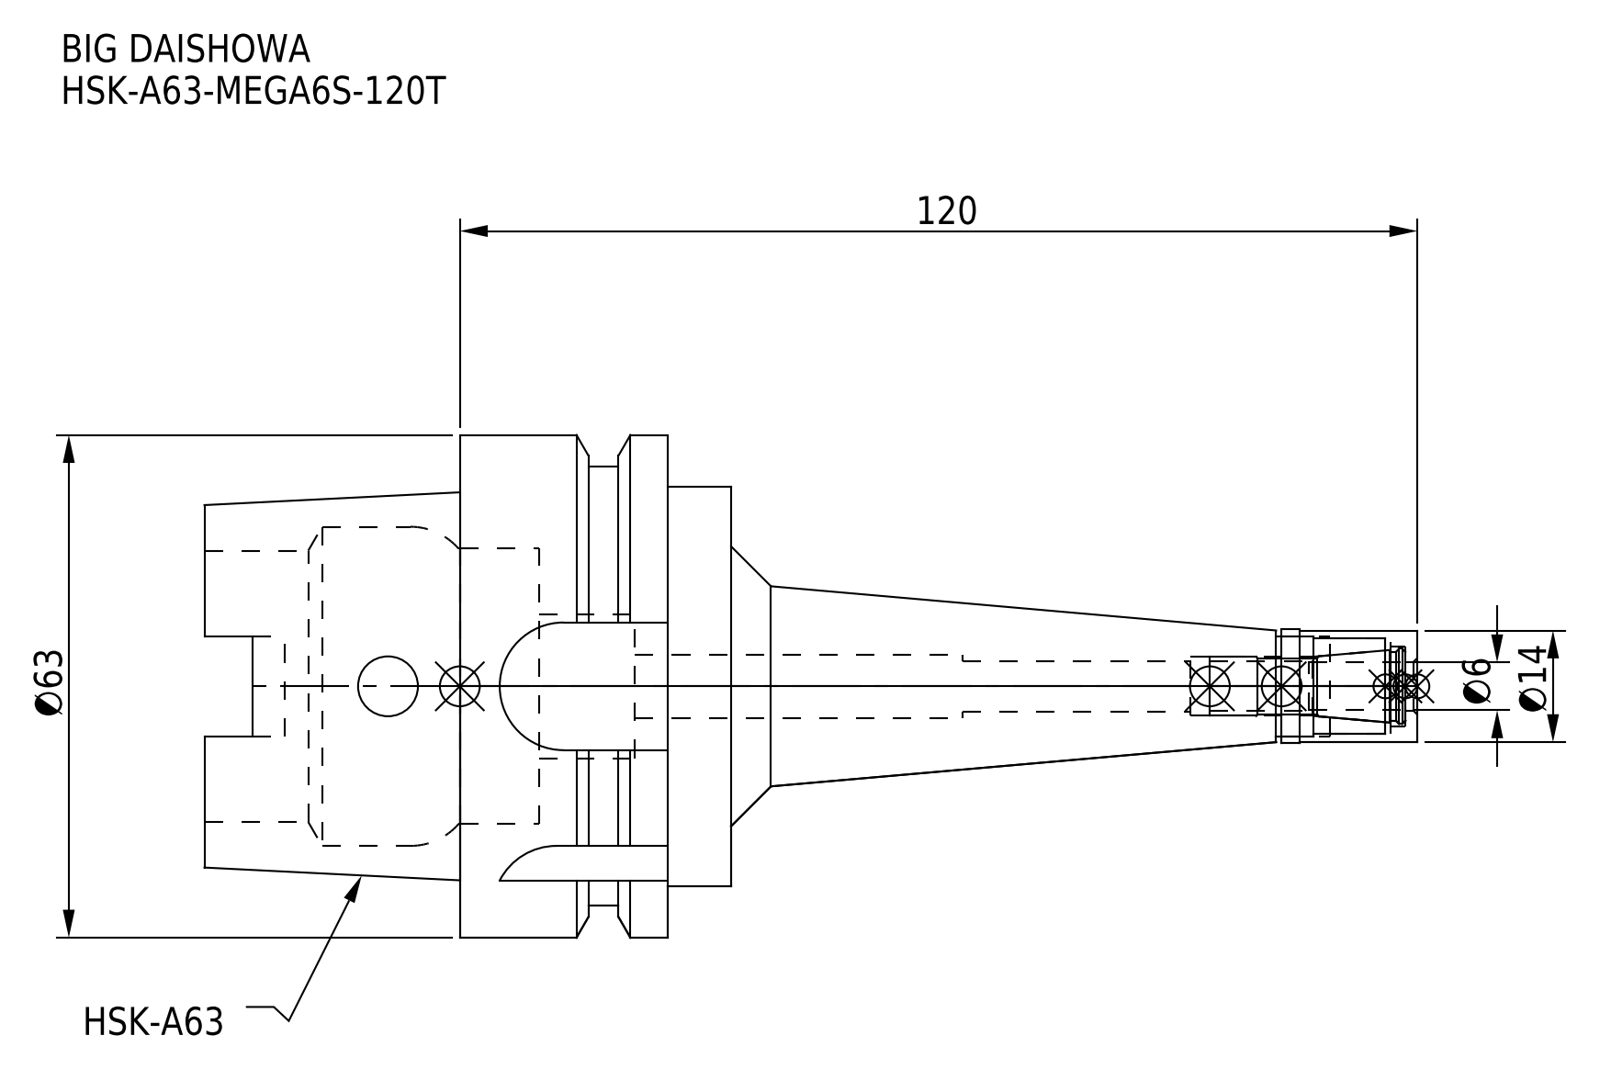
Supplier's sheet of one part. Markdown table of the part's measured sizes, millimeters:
| quantity | value |
| --- | --- |
| part name | HA63MS06120T-060_ASM.stp; HSK-A63-MEGA6S-120T-060.stp; MGN6S_1.stp; HSK-A63-MEGA6S-120T_1.stp (+3 more) |
| STEP written by | SolidWorks 2019 (CONFIG_CONTROL_DESIGN) |
| units | millimeters |
| bodies | 2 solids, 122 faces (47 planar, 53 cylindrical, 22 other) |
| overall size | 152 × 63 × 63 |
| volume | 118 949 mm³ |
| surface area | 31 587 mm² |
| round holes (diameter × count) | 6.1 × 1, 6.4 × 1, 7.4 × 1, 7.5 × 1, 8 × 1, 10 × 1, 12 × 1, 12.5 × 1, 18 × 1, 34 × 1, 34.5 × 1, 40 × 1 |
| round bosses / shafts (diameter × count) | 63 × 1, 55 × 1, 50 × 1, 14.3 × 1, 14 × 1 |
| partial cylindrical surfaces (radius × count) | 2.88 × 4, 8 × 4 |
| main face-to-face distances | 26, 34, 8, 24.05, 16.05, 9.95, 58, 66, 41.95, 32 |
